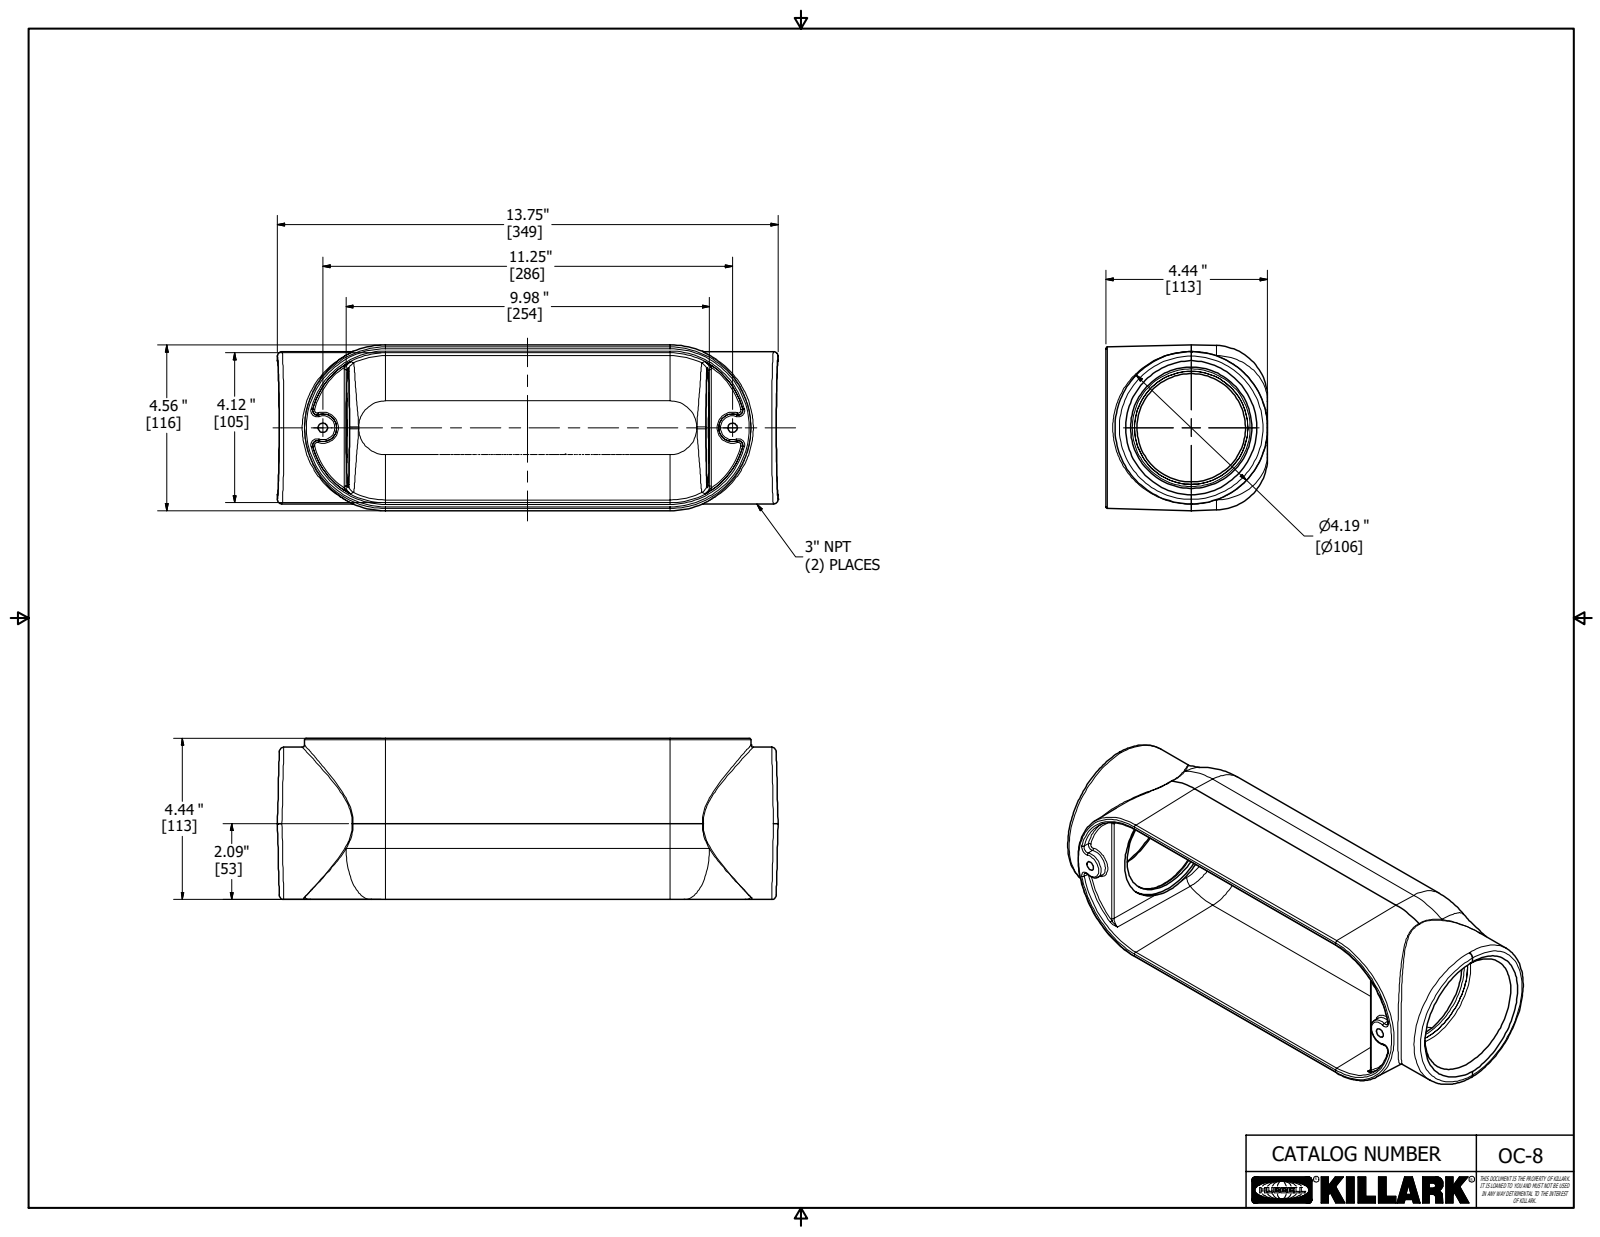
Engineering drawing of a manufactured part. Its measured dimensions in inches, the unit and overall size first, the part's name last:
Units: inches
Overall size (bounding box): 13.75 × 4.56 × 4.438
Round holes (diameter × count): ⌀0.257 ×2, ⌀3.297 ×2, ⌀0.333 ×1, ⌀2.98 ×1
Round bosses / shafts (diameter × count): ⌀4.187 ×1, ⌀0.5 ×1
Partial cylindrical surfaces — rounded edges, fillets, slot ends (radius × count): R0.047 ×30, R0.25 ×2, R1.244 ×2, R1.437 ×2, R0.021 ×1, R0.042 ×1, R0.114 ×1, R0.16 ×1
Main face-to-face distances: 4.281, 0.187, 0.278, 4.56, 0.031, 4.187, 0.07, 4, 0.25, 4.437
Hole centre spacings: 3.636, 7.615, 11.25
Volume: 49.67 in³ · Surface area: 355.2 in²
Bodies: 1 solid, 1135 faces (548 planar, 71 cylindrical, 516 other)
Part name (STEP PRODUCT): 5884-1 OC-8
STEP written by: Autodesk Inventor 2018 (AUTOMOTIVE_DESIGN)
